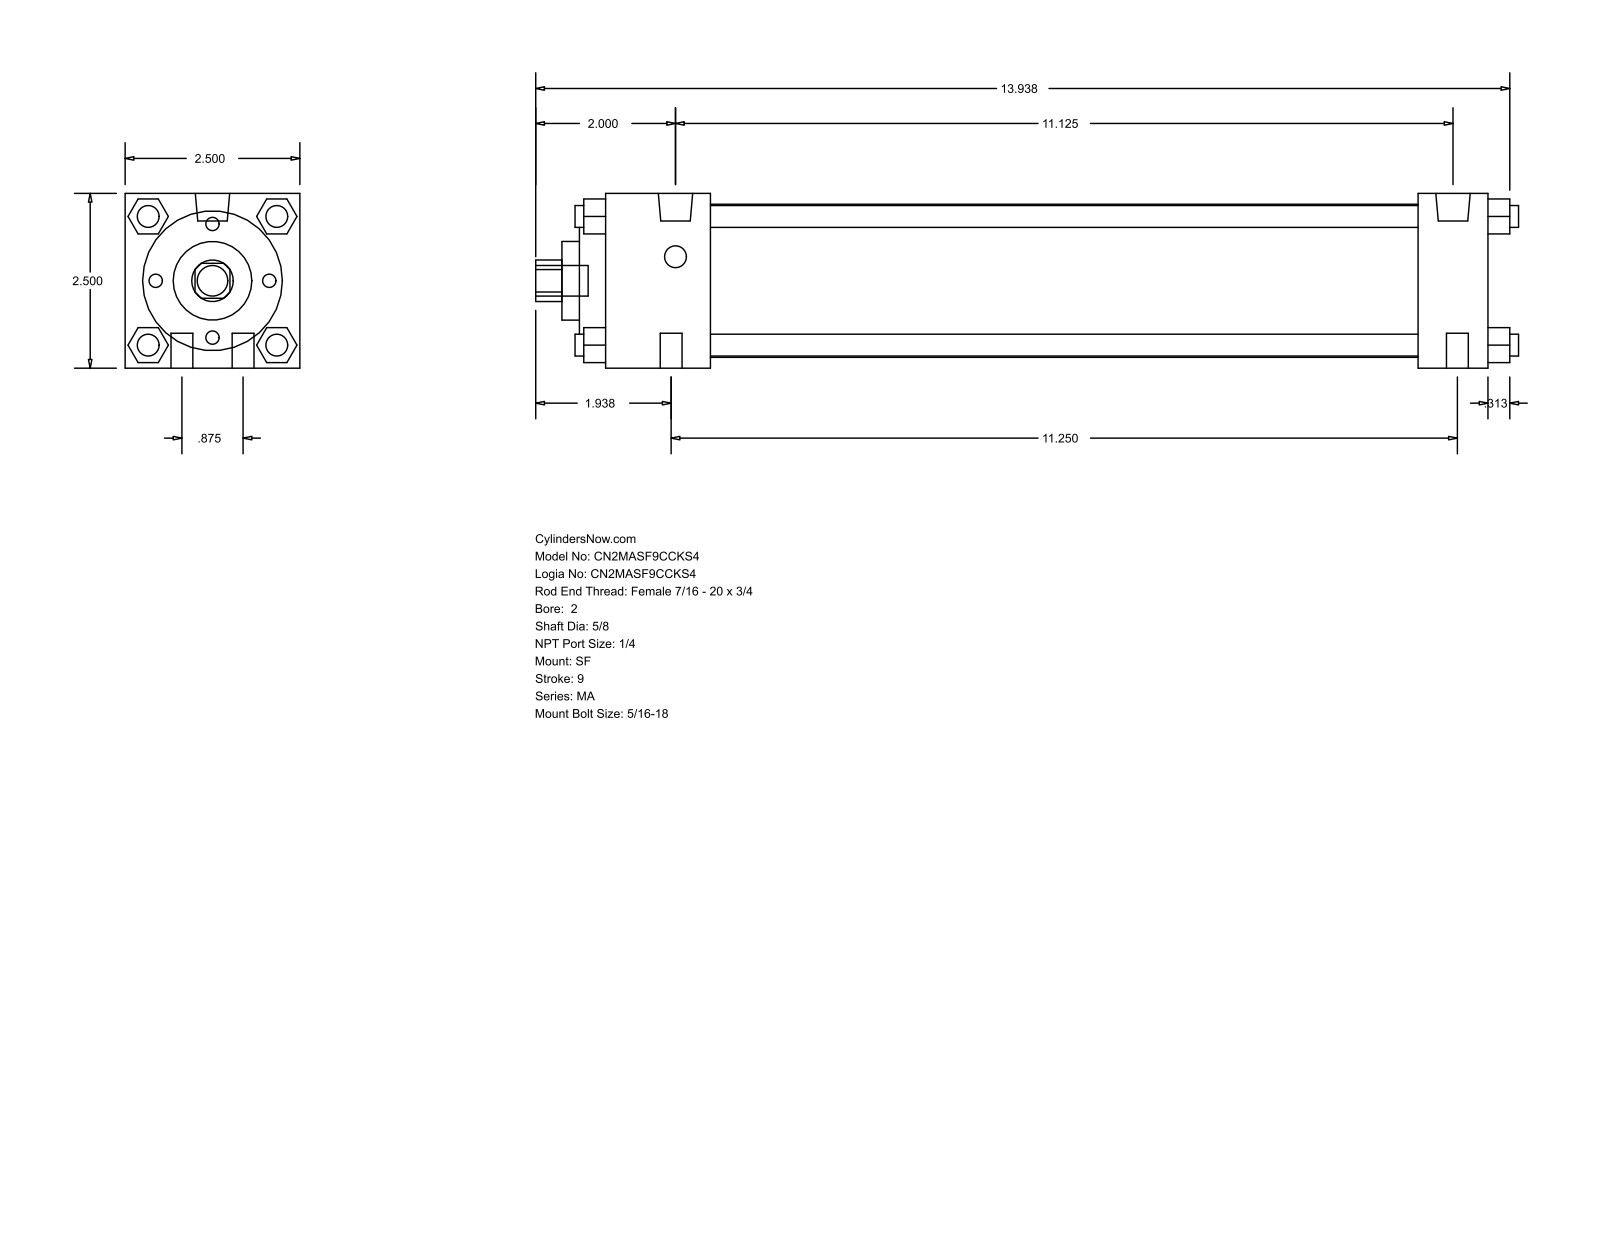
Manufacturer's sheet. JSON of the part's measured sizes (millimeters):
{"part_name": "MA_SF__0200_0.625", "step_written_by": "GSSL Pune (CONFIG_CONTROL_DESIGN)", "units": "millimeters", "bodies": {"solids": 0, "faces": 126, "planar": 95, "cylindrical": 31, "other": 0}, "overall_size": [357.19, 63.5, 63.5], "round_holes": [[15.88, 1], [28.57, 1], [50.8, 1], [55.63, 1]], "round_bosses_or_shafts": [[7.94, 10], [12.49, 2], [11.11, 1]], "partial_cylinders_radius": [[7.54, 1]], "face_to_face_distances": [63.5, 12.7, 38.1, 9.52, 320.67, 295.28, 25.39, 257.18, 282.57, 47.62]}
